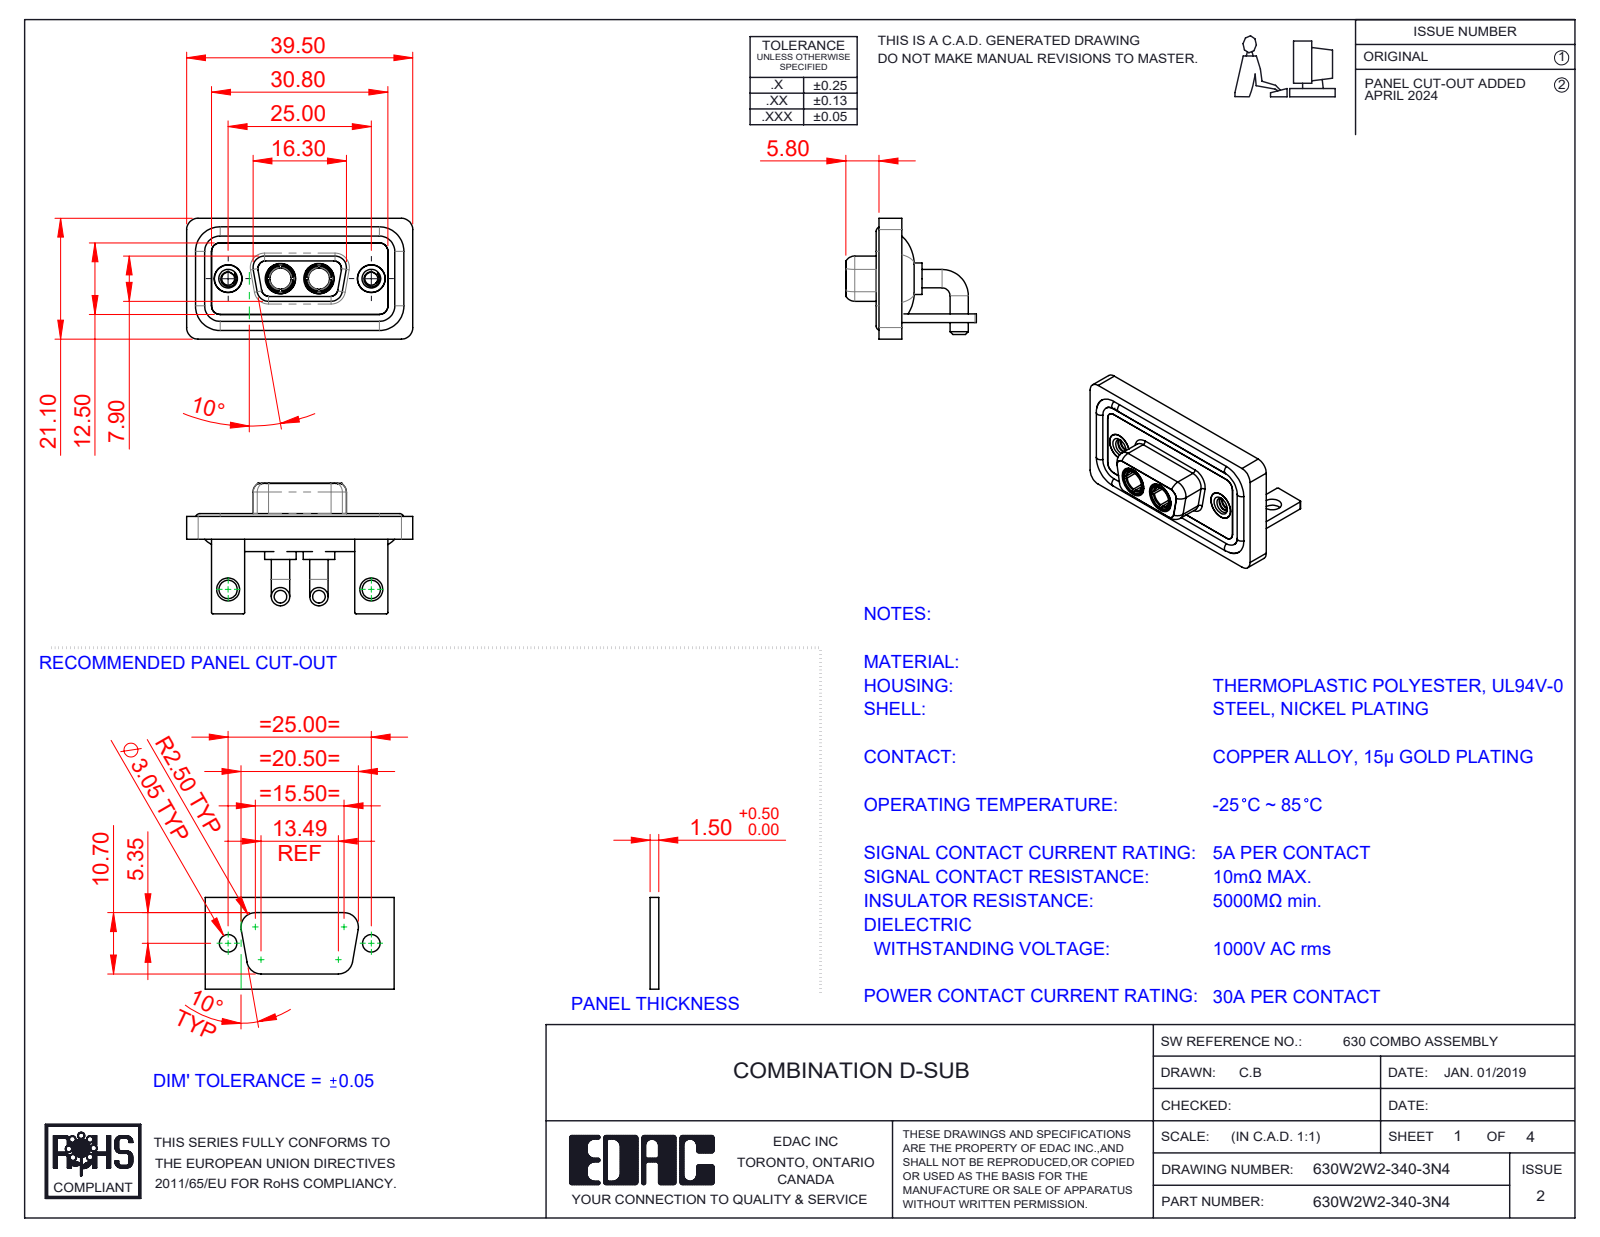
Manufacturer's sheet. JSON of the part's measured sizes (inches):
{"part_name": "630Combo Waterproof Housing_09 Contacts; 630Combo Shell Rear_09 Contacts; 630Combo Threaded Rivet_2; 630Combo Stabilizer Bracket_50 Contacts (+4 more)", "step_written_by": "SolidWorks 2023 (CONFIG_CONTROL_DESIGN)", "units": "inches", "bodies": {"solids": 13, "faces": 590, "planar": 183, "cylindrical": 262, "other": 145}, "overall_size": [1.555, 0.898, 0.831], "volume_in3": 0.32, "surface_area_in2": 13.26, "round_holes": [[0.191, 4], [0.089, 2], [0.126, 2], [0.146, 2], [0.157, 2], [0.159, 2], [0.197, 2], [0.209, 2]], "round_bosses_or_shafts": [[0.126, 4], [0.063, 4], [0.217, 2], [0.205, 2], [0.195, 2], [0.195, 2], [0.189, 2], [0.187, 2]], "partial_cylinders_radius": [[0.079, 19], [0.059, 18], [0.01, 16], [0.053, 8], [0.063, 8], [0.02, 5], [0.024, 4], [0.026, 4]], "face_to_face_distances": [0.016, 0.114, 0.059, 0.071, 0.043, 0.146, 0.031, 0.098, 0.063, 0.122], "hole_center_spacings": [0.36, 0.624, 0.984, 0.265]}
